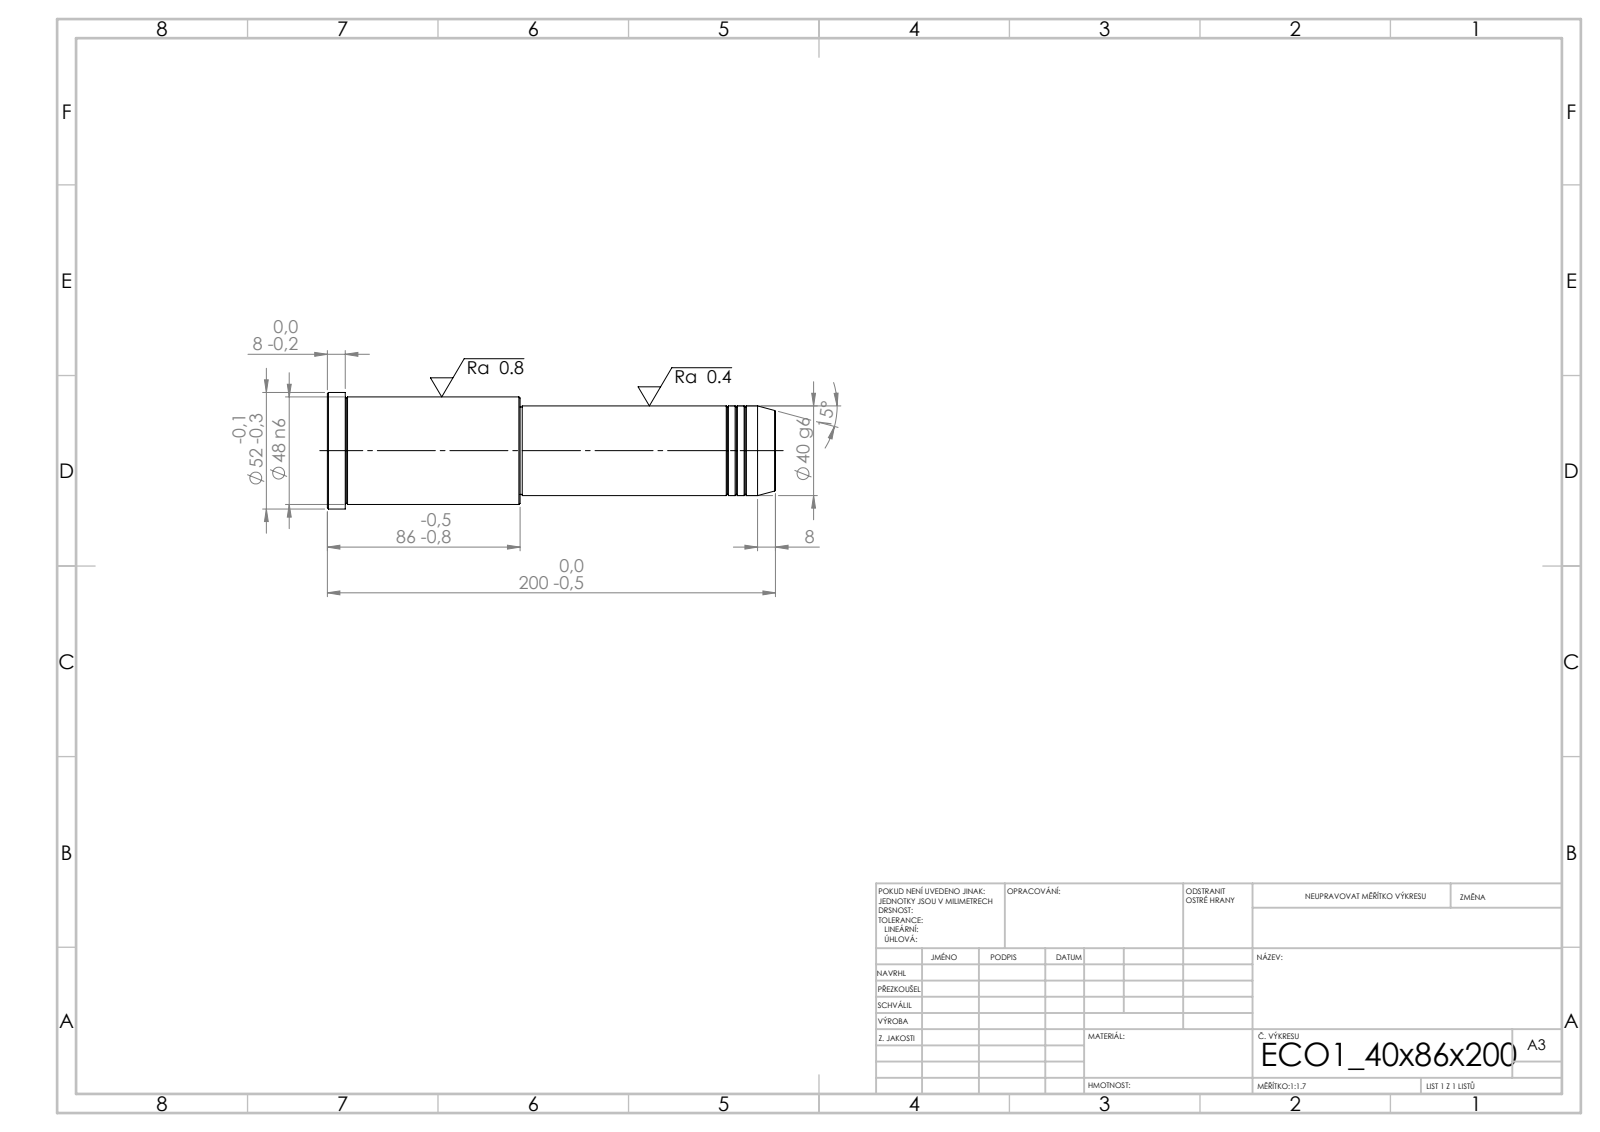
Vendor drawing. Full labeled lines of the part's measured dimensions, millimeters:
STEP written by: SolidWorks 2019 (CONFIG_CONTROL_DESIGN)
Units: millimetres
Bodies: 1 solid, 43 faces (5 planar, 14 cylindrical, 24 other)
Overall size (bounding box): 200 × 52 × 52
Volume: 300 043 mm³ · Surface area: 31 671 mm²
Round bosses / shafts (diameter × count): ⌀52 ×1, ⌀48 ×1, ⌀40 ×1, ⌀39 ×1
Main face-to-face distances: 200, 114, 86, 192, 78, 8, 113, 1, 79, 87
